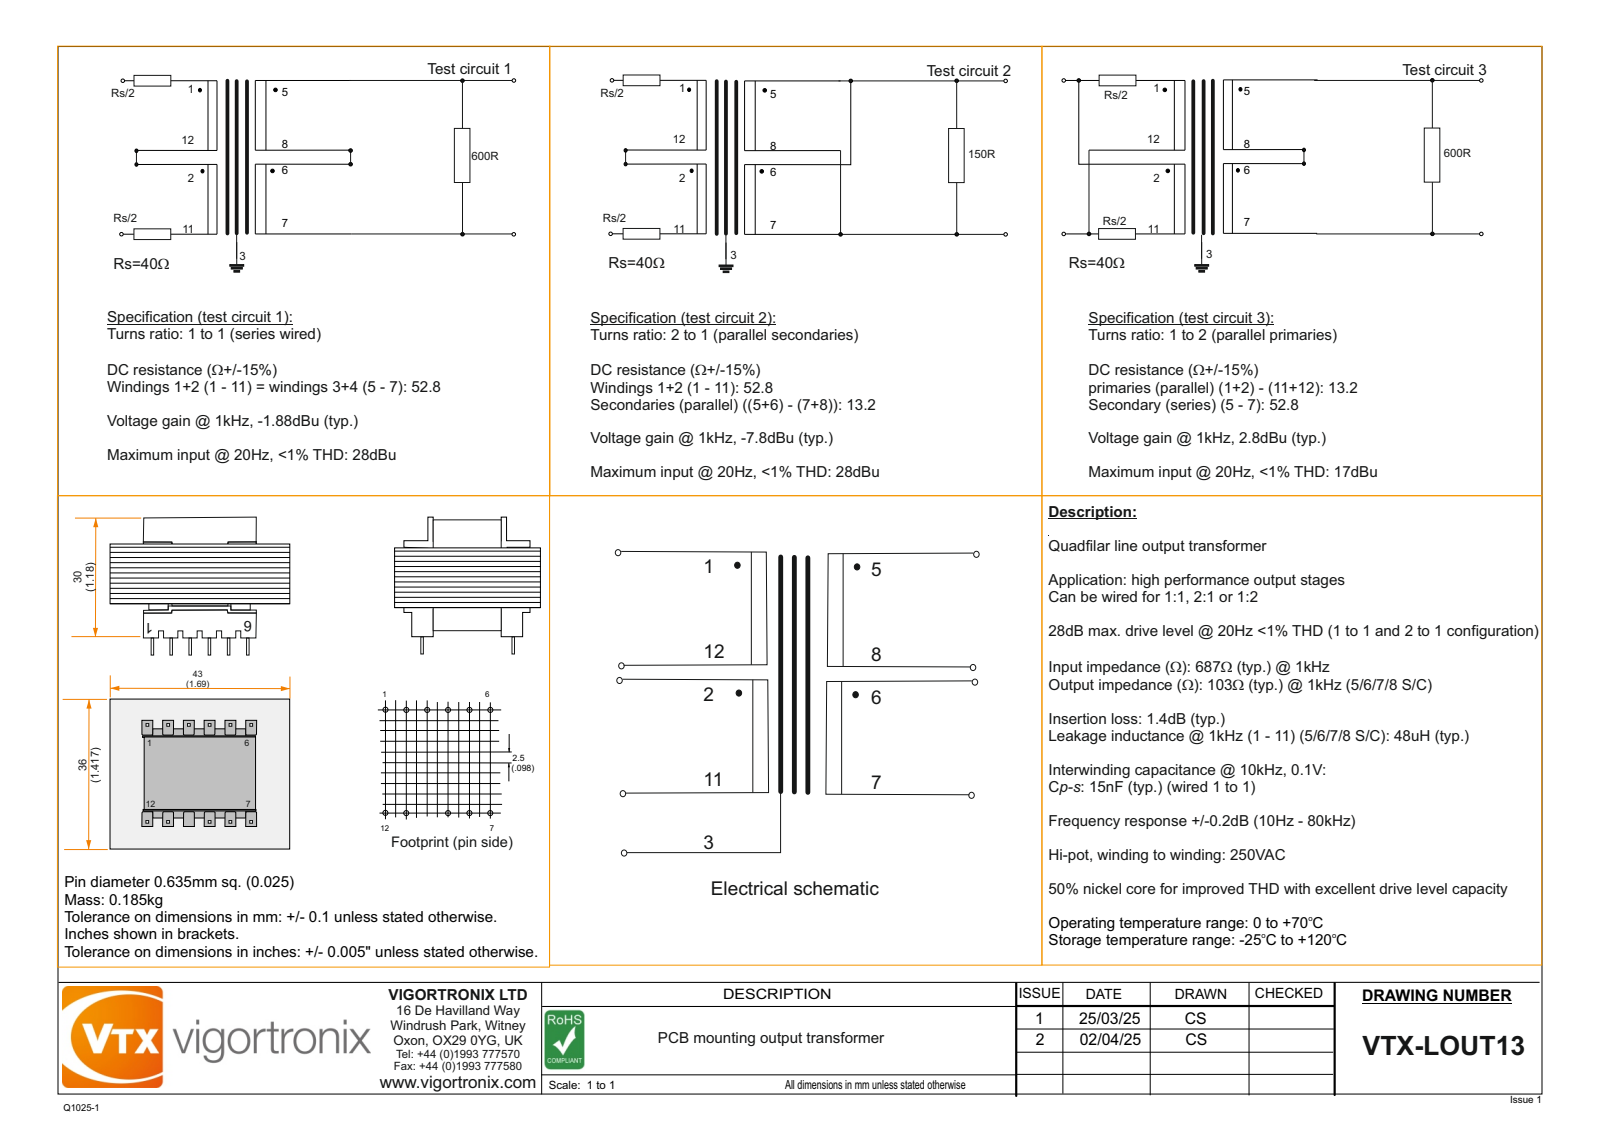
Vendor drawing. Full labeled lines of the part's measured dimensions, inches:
Part name (STEP PRODUCT): EI42 Windings; E42; Bobbin EI 42 X 14.8; I42 (+2 more)
STEP written by: SolidWorks 2024 (AUTOMOTIVE_DESIGN)
Units: inches
Bodies: 85 solids, 1162 faces (1034 planar, 128 cylindrical, 0 other)
Overall size (bounding box): 1.654 × 1.394 × 1.372
Volume: 1.66 in³ · Surface area: 154.9 in²
Partial cylindrical surfaces — rounded edges, fillets, slot ends (radius × count): R0.01 ×56, R0.137 ×20, R0.276 ×4, R0.039 ×2, R0.098 ×2
Main face-to-face distances: 0.016, 0.031, 0.047, 0.063, 0.079, 0.094, 0.11, 0.126, 0.142, 0.157
